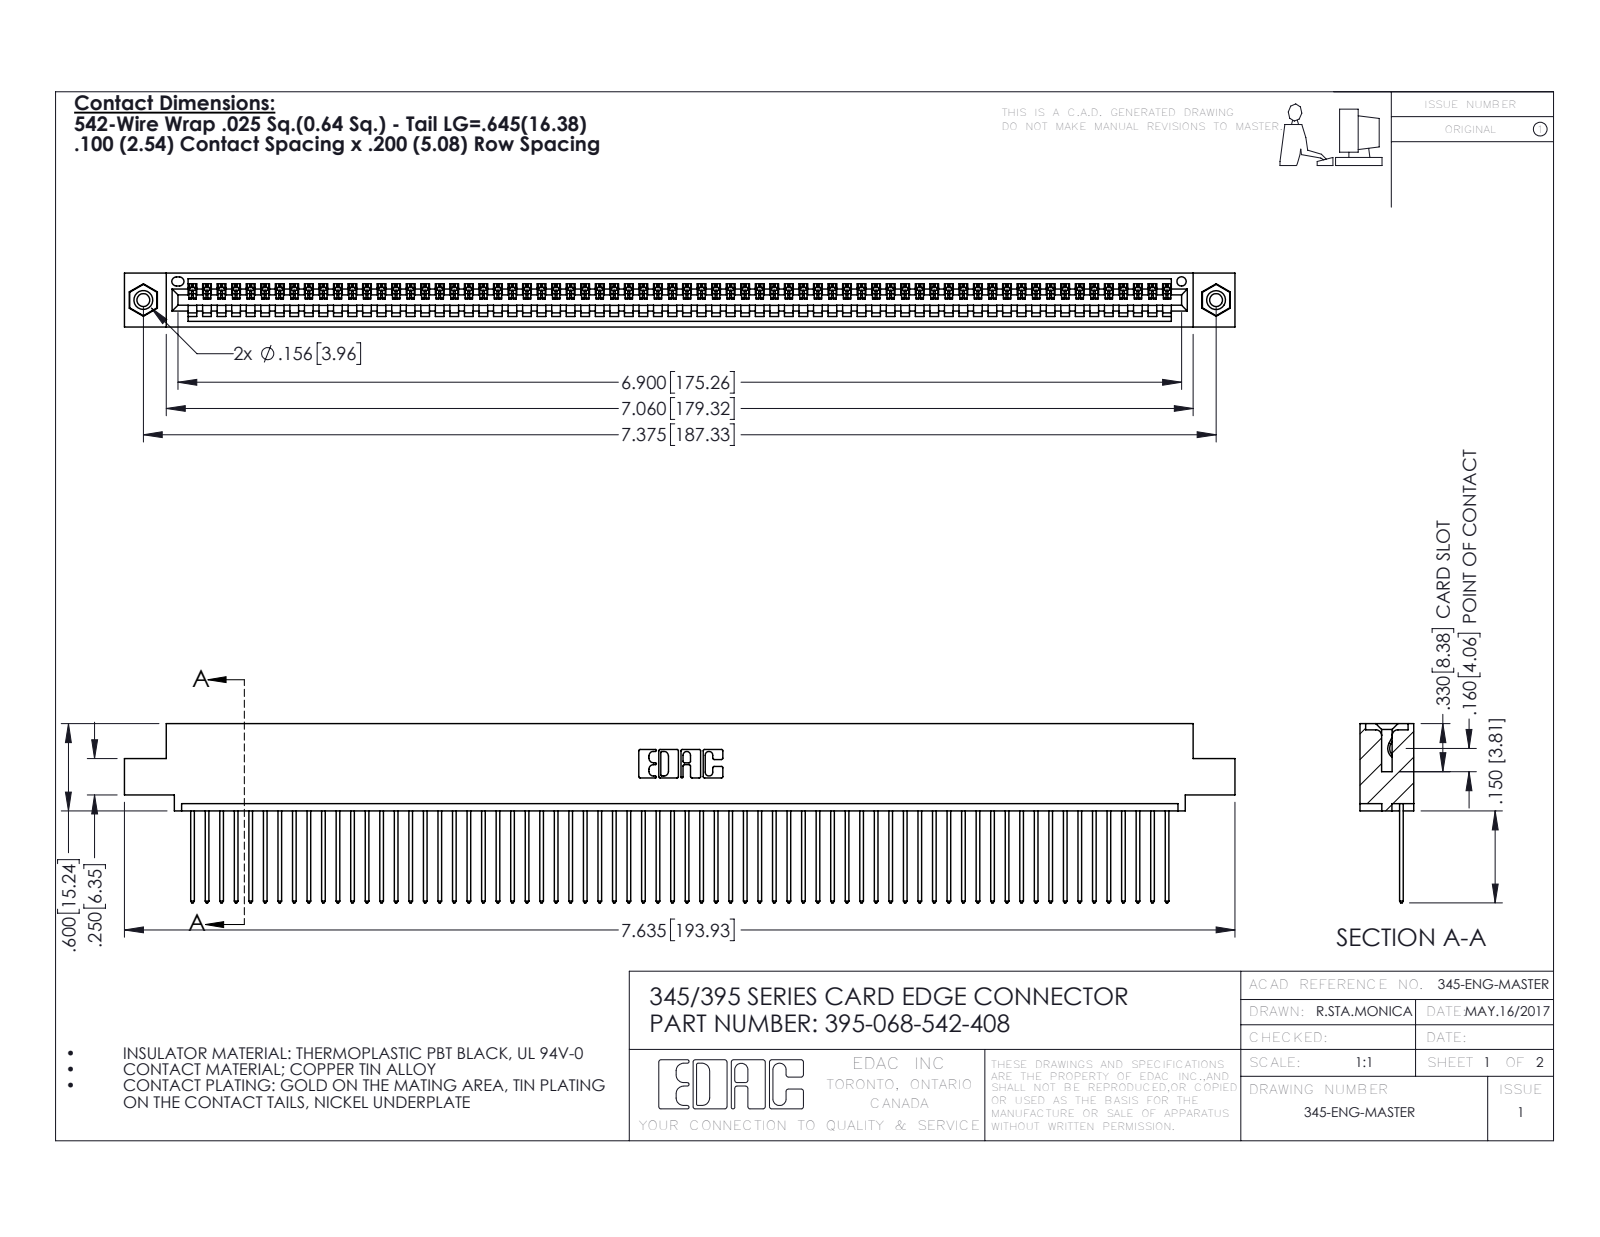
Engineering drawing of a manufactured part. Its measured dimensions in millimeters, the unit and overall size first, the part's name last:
Units: millimetres
Overall size (bounding box): 193.9 × 31.3 × 9.4
Round holes (diameter × count): ⌀2.3 ×2, ⌀3.2 ×2, ⌀4 ×2, ⌀1.6 ×1
Round bosses / shafts (diameter × count): ⌀3.9 ×2
Partial cylindrical surfaces — rounded edges, fillets, slot ends (radius × count): R0.2 ×136, R0.3 ×136, R0.3 ×22, R0.2 ×6, R0.8 ×6, R0.7 ×3, R0.8 ×2, R1 ×2
Main face-to-face distances: 1.8, 7.6, 2.5, 6.9, 0.6, 9.4, 5.1, 5.7, 3.8, 1.8
Hole centre spacings: 6.9, 181.3, 187.3
Volume: 18 700 mm³ · Surface area: 26 260 mm²
Bodies: 71 solids, 4134 faces (2836 planar, 1282 cylindrical, 16 other)
Part name (STEP PRODUCT): 345 Part_0.110 Offset - 0.156 Dia-TI; 345-250-001_345-250-003-102; 395-068-542-408; 345-292-001_345-293-142
STEP written by: SolidWorks 2016 (CONFIG_CONTROL_DESIGN)
